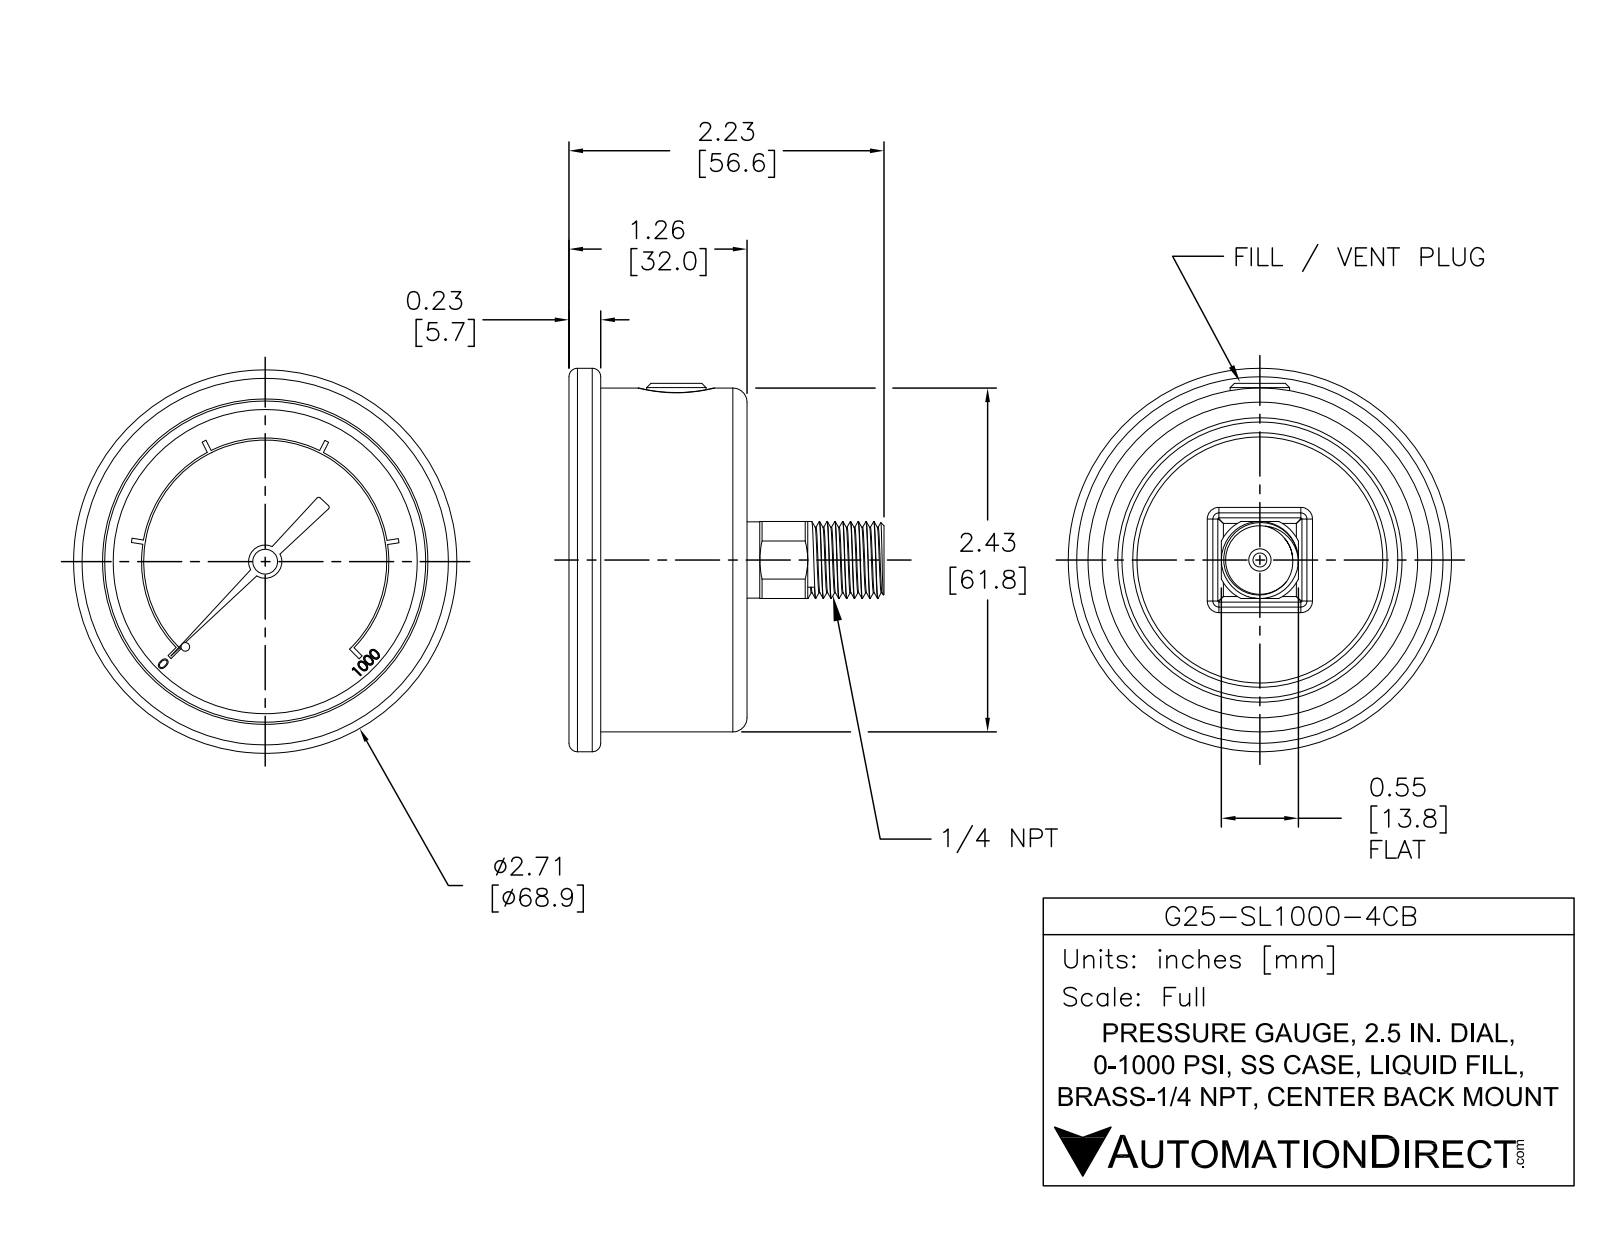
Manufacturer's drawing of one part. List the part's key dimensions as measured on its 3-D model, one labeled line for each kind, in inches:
Part name (STEP PRODUCT): G25-SL1000-4CB
STEP written by: SolidWorks 2021 (AUTOMOTIVE_DESIGN)
Units: inches
Bodies: 1 solid, 359 faces (210 planar, 83 cylindrical, 66 other)
Overall size (bounding box): 2.713 × 2.713 × 2.23
Volume: 5.168 in³ · Surface area: 24.83 in²
Round holes (diameter × count): ⌀0.071 ×1, ⌀0.098 ×1, ⌀2.272 ×1
Round bosses / shafts (diameter × count): ⌀2.713 ×1, ⌀2.433 ×1, ⌀0.545 ×1, ⌀0.54 ×1, ⌀0.42 ×1, ⌀0.235 ×1, ⌀0.176 ×1, ⌀0.14 ×1
Partial cylindrical surfaces — rounded edges, fillets, slot ends (radius × count): R0.06 ×8, R0.015 ×2, R0.304 ×1, R0.86 ×1, R0.875 ×1
Main face-to-face distances: 0.95, 1.2, 0.25, 0.06, 1.01, 1.26, 1.035, 0.975, 0.025, 0.225
